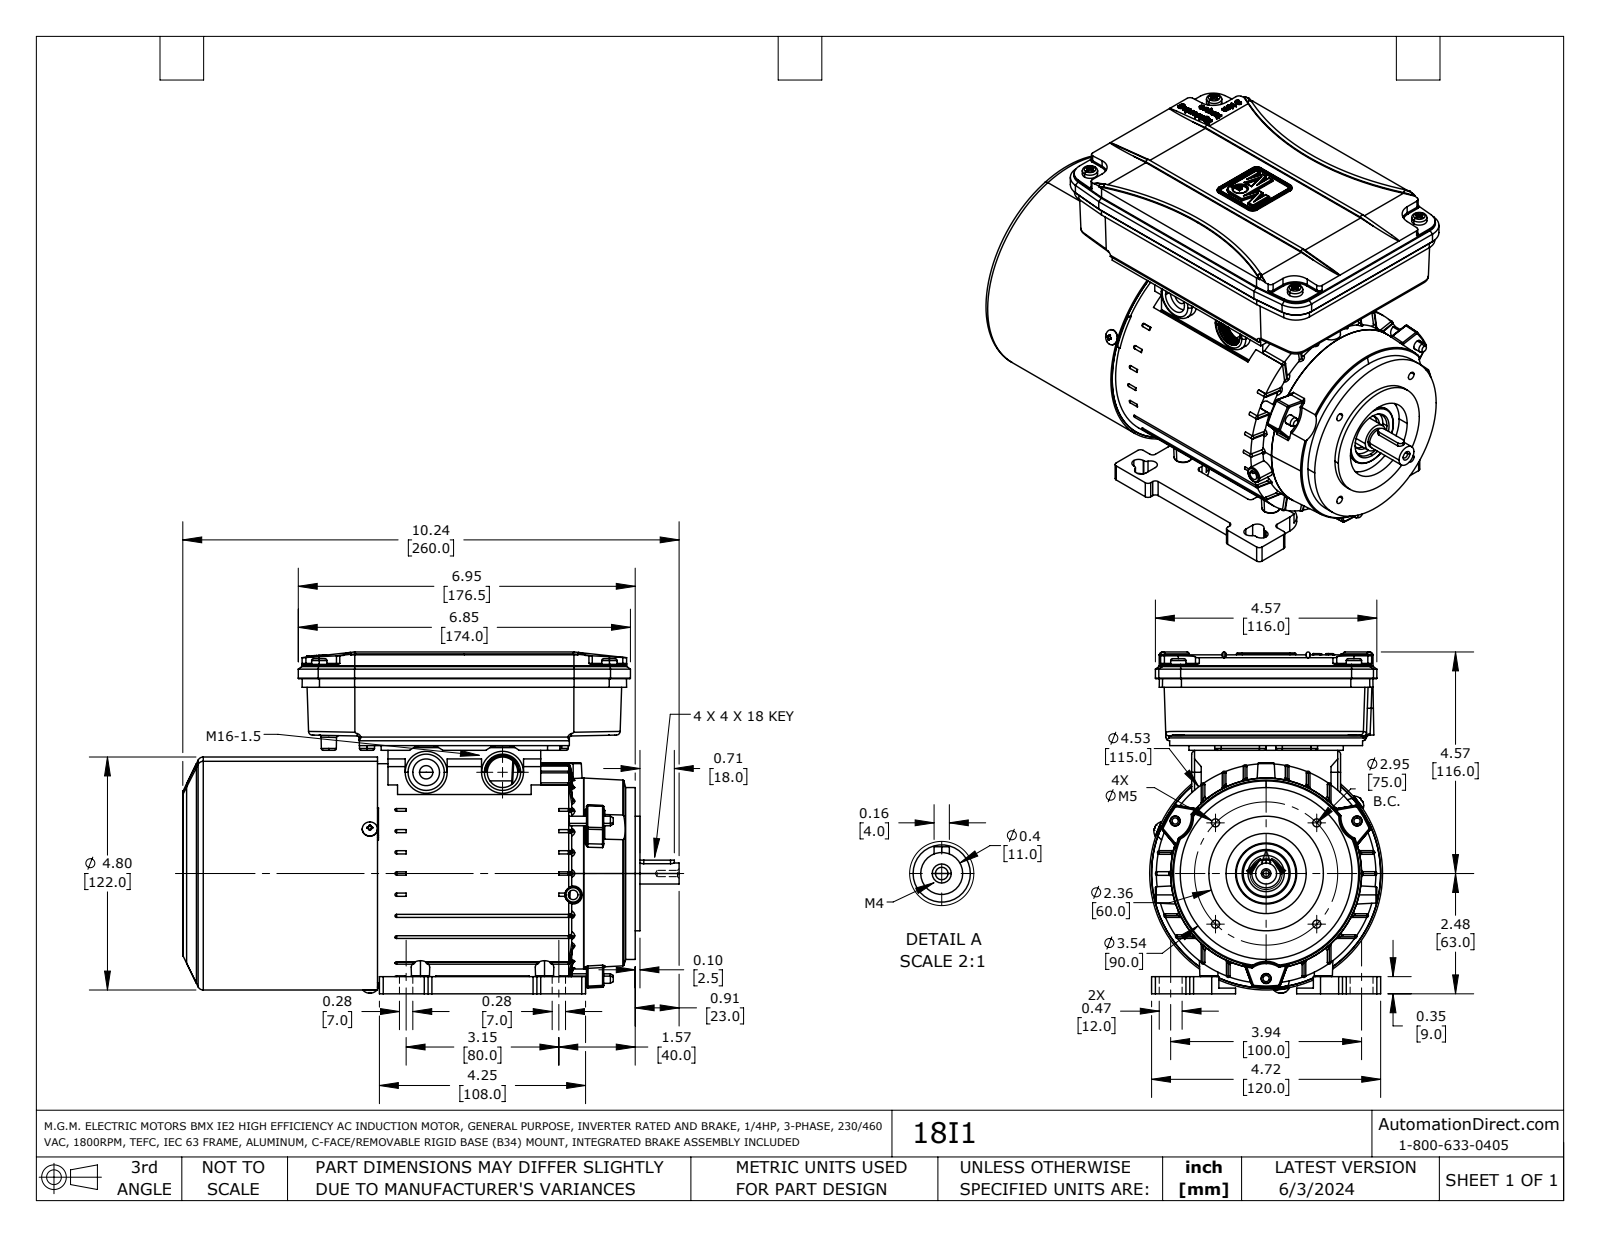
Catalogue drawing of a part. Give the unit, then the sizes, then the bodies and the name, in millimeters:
Units: millimetres
Overall size (bounding box): 260 × 179 × 122
Round holes (diameter × count): ⌀3.3 ×15, ⌀4.5 ×12, ⌀4 ×11, ⌀2.5 ×7, ⌀3 ×4, ⌀4.2 ×4, ⌀5.5 ×4, ⌀6 ×4, ⌀6.5 ×4, ⌀10 ×4, ⌀5 ×2, ⌀8 ×2
Round bosses / shafts (diameter × count): ⌀4.5 ×8, ⌀3 ×8, ⌀8 ×7, ⌀5 ×7, ⌀9.8 ×4, ⌀2 ×3, ⌀122 ×1, ⌀115 ×1
Partial cylindrical surfaces — rounded edges, fillets, slot ends (radius × count): R1 ×252, R2 ×59, R0.2 ×56, R0.5 ×56, R0.4 ×36, R0.3 ×24, R0.1 ×16, R2.2 ×16
Main face-to-face distances: 2, 9, 2, 7, 168.5, 30.9, 37.9, 39.9, 28.9, 9
Hole centre spacings: 31, 37.5, 40, 42.7, 53, 70.4, 73.1, 74.8
Volume: 2 555 000 mm³ · Surface area: 447 200 mm²
Bodies: 12 solids, 3503 faces (1148 planar, 1208 cylindrical, 1147 other)
Part name (STEP PRODUCT): 18I1
STEP written by: SolidWorks 2021 (AUTOMOTIVE_DESIGN)
